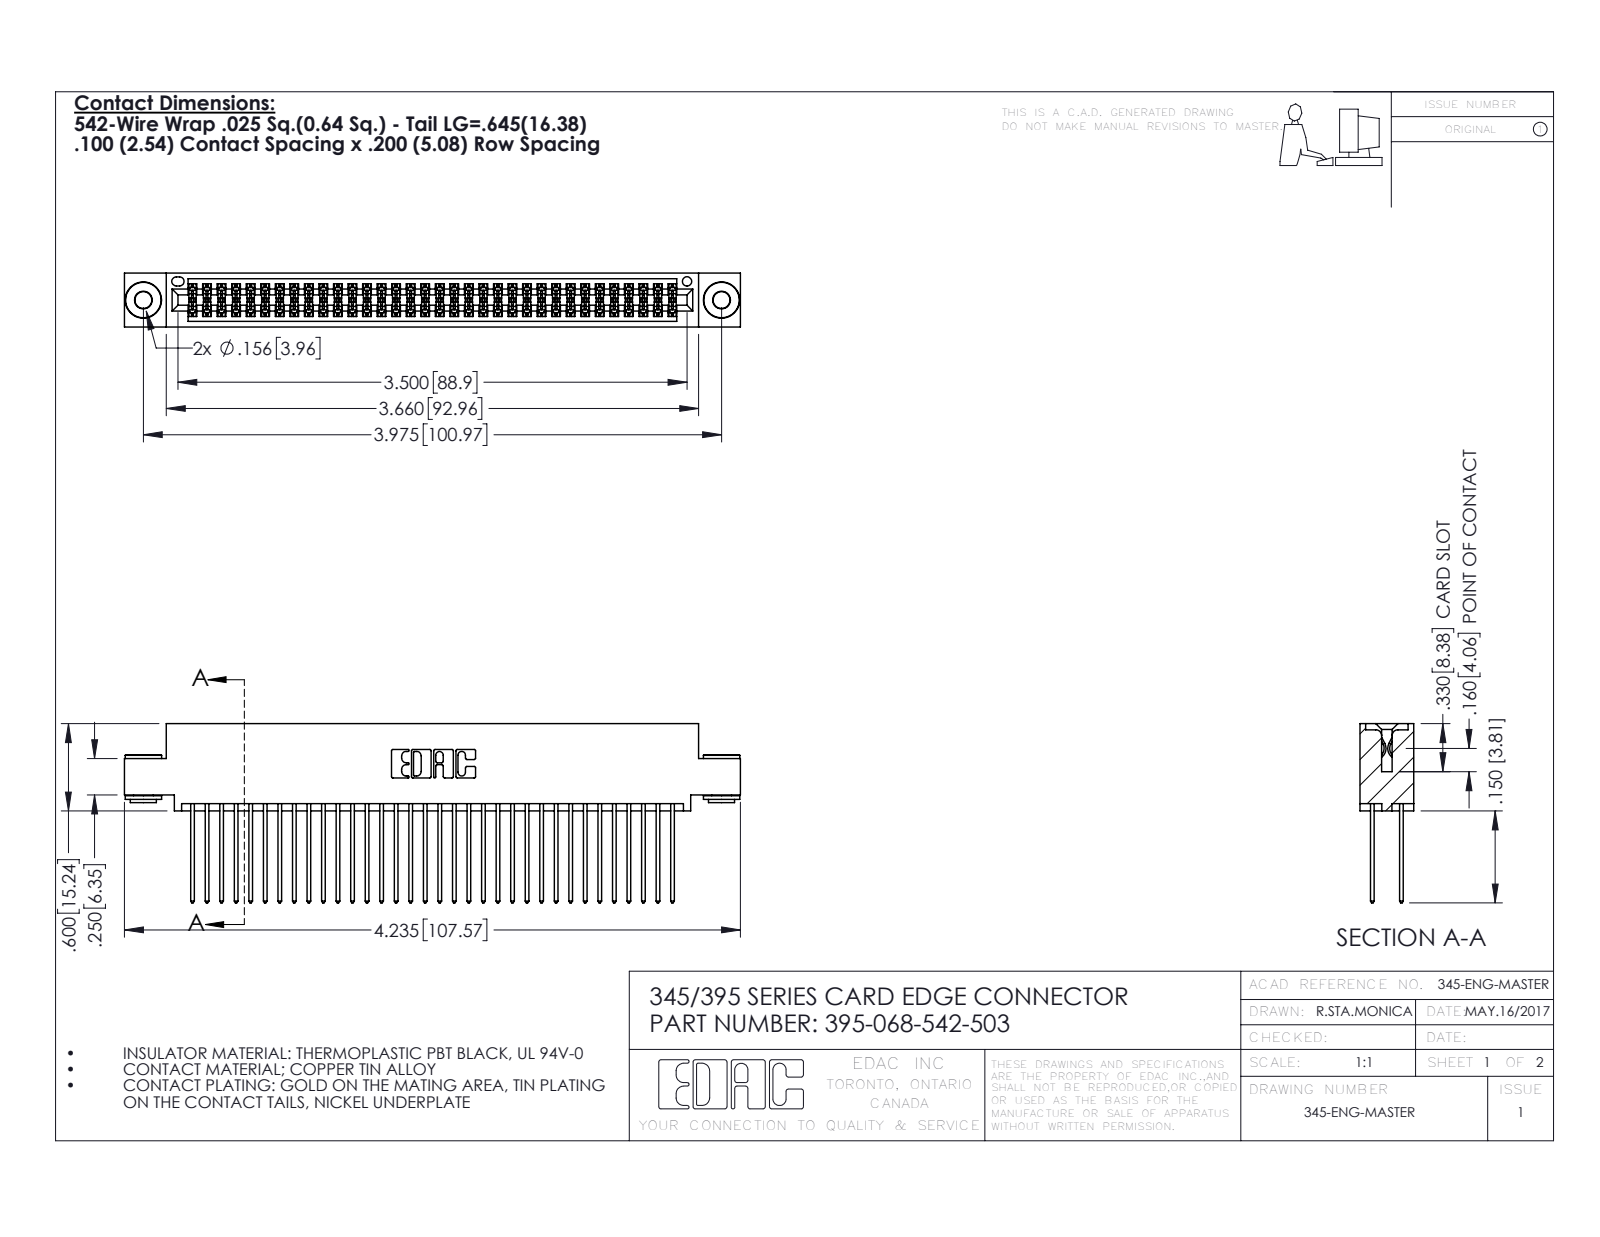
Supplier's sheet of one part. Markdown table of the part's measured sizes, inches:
| quantity | value |
| --- | --- |
| part name | 345-292-001_345-293-142; 395-068-542-503; 345 Part_0.110 Offset - 0.156 Dia-TH; 345-250-002_345-250-002-102 |
| STEP written by | SolidWorks 2016 (CONFIG_CONTROL_DESIGN) |
| units | inches |
| bodies | 71 solids, 3568 faces (2338 planar, 1222 cylindrical, 8 other) |
| overall size | 4.235 × 1.232 × 0.37 |
| volume | 0.649 in³ |
| surface area | 26.89 in² |
| round holes (diameter × count) | 0.116 × 2, 0.156 × 2, 0.064 × 1 |
| round bosses / shafts (diameter × count) | 0.25 × 2, 0.18 × 2, 0.136 × 2 |
| partial cylindrical surfaces (radius × count) | 0.006 × 102, 0.01 × 68, 0.01 × 22, 0.007 × 6, 0.031 × 6, 0.026 × 3, 0.014 × 2, 0.019 × 2 |
| main face-to-face distances | 0.072, 0.298, 0.2, 0.025, 0.098, 0.272, 0.37, 0.225, 0.175, 0.149 |
| hole center spacings | 0.27, 3.74, 3.975 |
